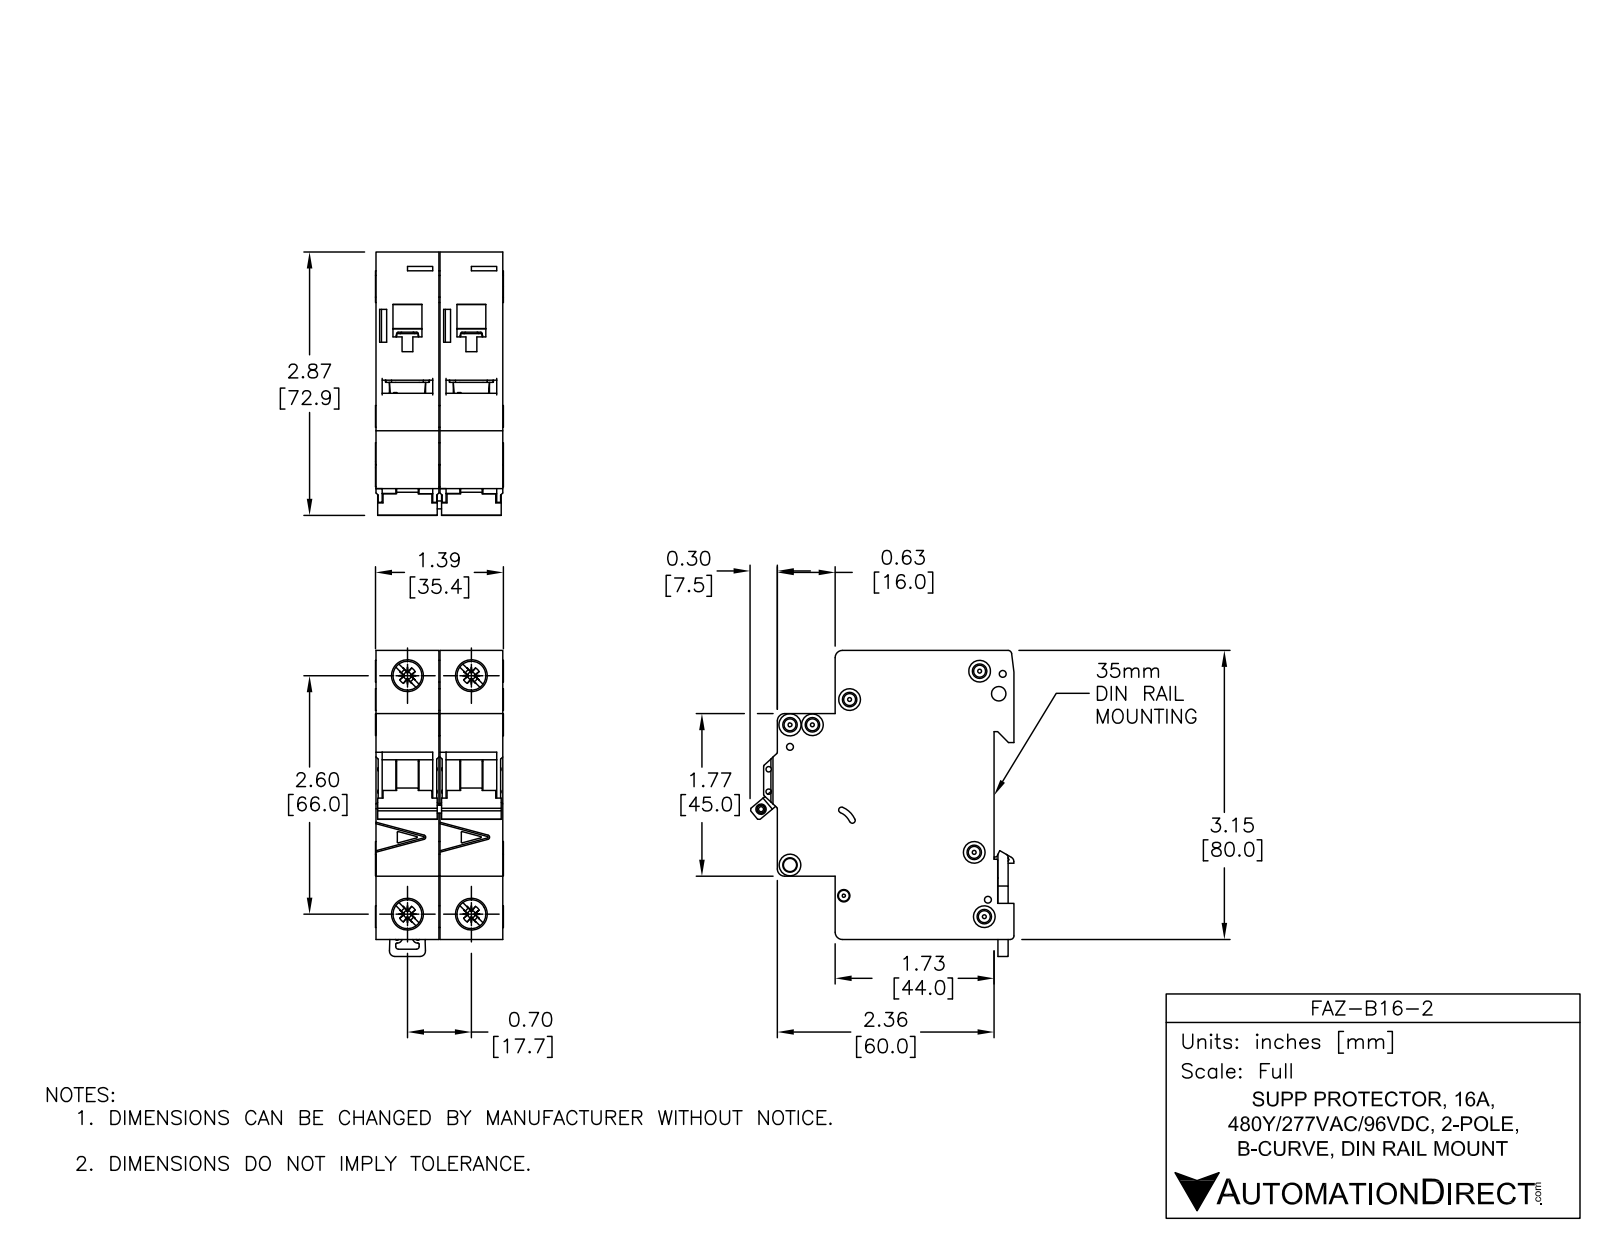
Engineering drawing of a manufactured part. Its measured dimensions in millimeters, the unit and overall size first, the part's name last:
Units: millimetres
Overall size (bounding box): 84.78 × 73.04 × 35.4
Round holes (diameter × count): ⌀3.6 ×6, ⌀1.9 ×3, ⌀1.09 ×2, ⌀1.5 ×2, ⌀4 ×2, ⌀7.15 ×2, ⌀8.2 ×2, ⌀2.15 ×1, ⌀2.2 ×1, ⌀2.55 ×1, ⌀3.3 ×1, ⌀3.4 ×1
Round bosses / shafts (diameter × count): ⌀6 ×4, ⌀8.2 ×2, ⌀2.5 ×2
Partial cylindrical surfaces — rounded edges, fillets, slot ends (radius × count): R0.25 ×49, R0.5 ×19, R2 ×10, R0.2 ×8, R1 ×8, R0.8 ×2, R1.8 ×2, R3 ×2
Main face-to-face distances: 17.7, 17.5, 35.2, 79.48, 5.5, 49.5, 44, 65.5, 60, 16
Hole centre spacings: 6.2, 13.64, 17.7, 66, 68.33, 4.81, 5.19, 5.61
Volume: 149 808 mm³ · Surface area: 38 799 mm²
Bodies: 8 solids, 1104 faces (466 planar, 396 cylindrical, 242 other)
Part name (STEP PRODUCT): FAZ-B16-2
STEP written by: SolidWorks 2014 (AUTOMOTIVE_DESIGN)
